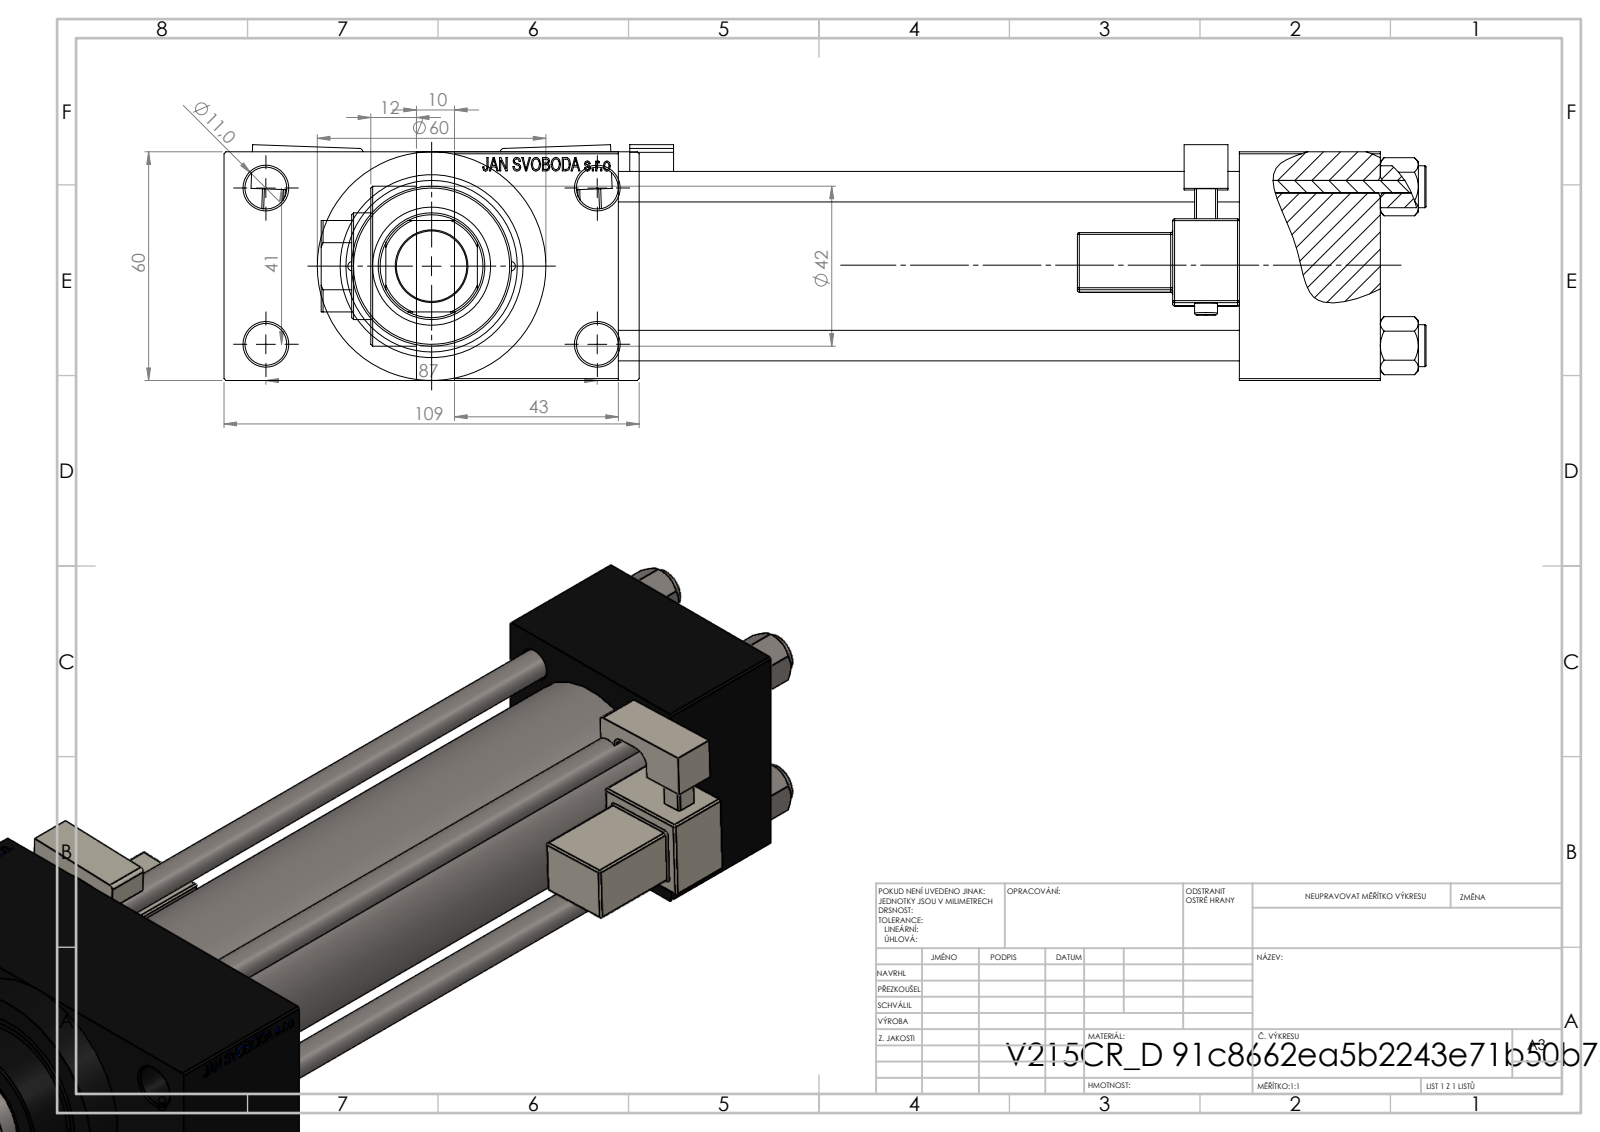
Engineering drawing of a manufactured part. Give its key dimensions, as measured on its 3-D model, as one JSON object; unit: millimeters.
{"part_name": "V215CR_D_TYCINKA; NUT_M5_D; V215_VC_A; V215CR_MSU (+2 more)", "step_written_by": "SolidWorks 2019 (CONFIG_CONTROL_DESIGN)", "units": "millimeters", "bodies": {"solids": 13, "faces": 1268, "planar": 560, "cylindrical": 152, "other": 556}, "overall_size": [290, 109, 61.9], "volume_mm3": 697820, "surface_area_mm2": 189324, "round_holes": [[8, 4], [11, 4], [2.5, 2], [7, 2], [16.66, 2], [24, 2], [18.5, 1], [28, 1], [31, 1], [40, 1], [45, 1]], "round_bosses_or_shafts": [[11, 4], [6, 2], [60, 1], [46, 1], [42, 1]], "partial_cylinders_radius": [[0.5, 48], [1, 2], [2.5, 2], [4, 2], [13.5, 1]], "face_to_face_distances": [60, 163, 24.5, 84.5, 37, 200, 243, 206, 43, 109], "hole_center_spacings": [20.85, 22.65, 29.49, 30.62, 41.7, 46.53, 47.15, 48.09]}
